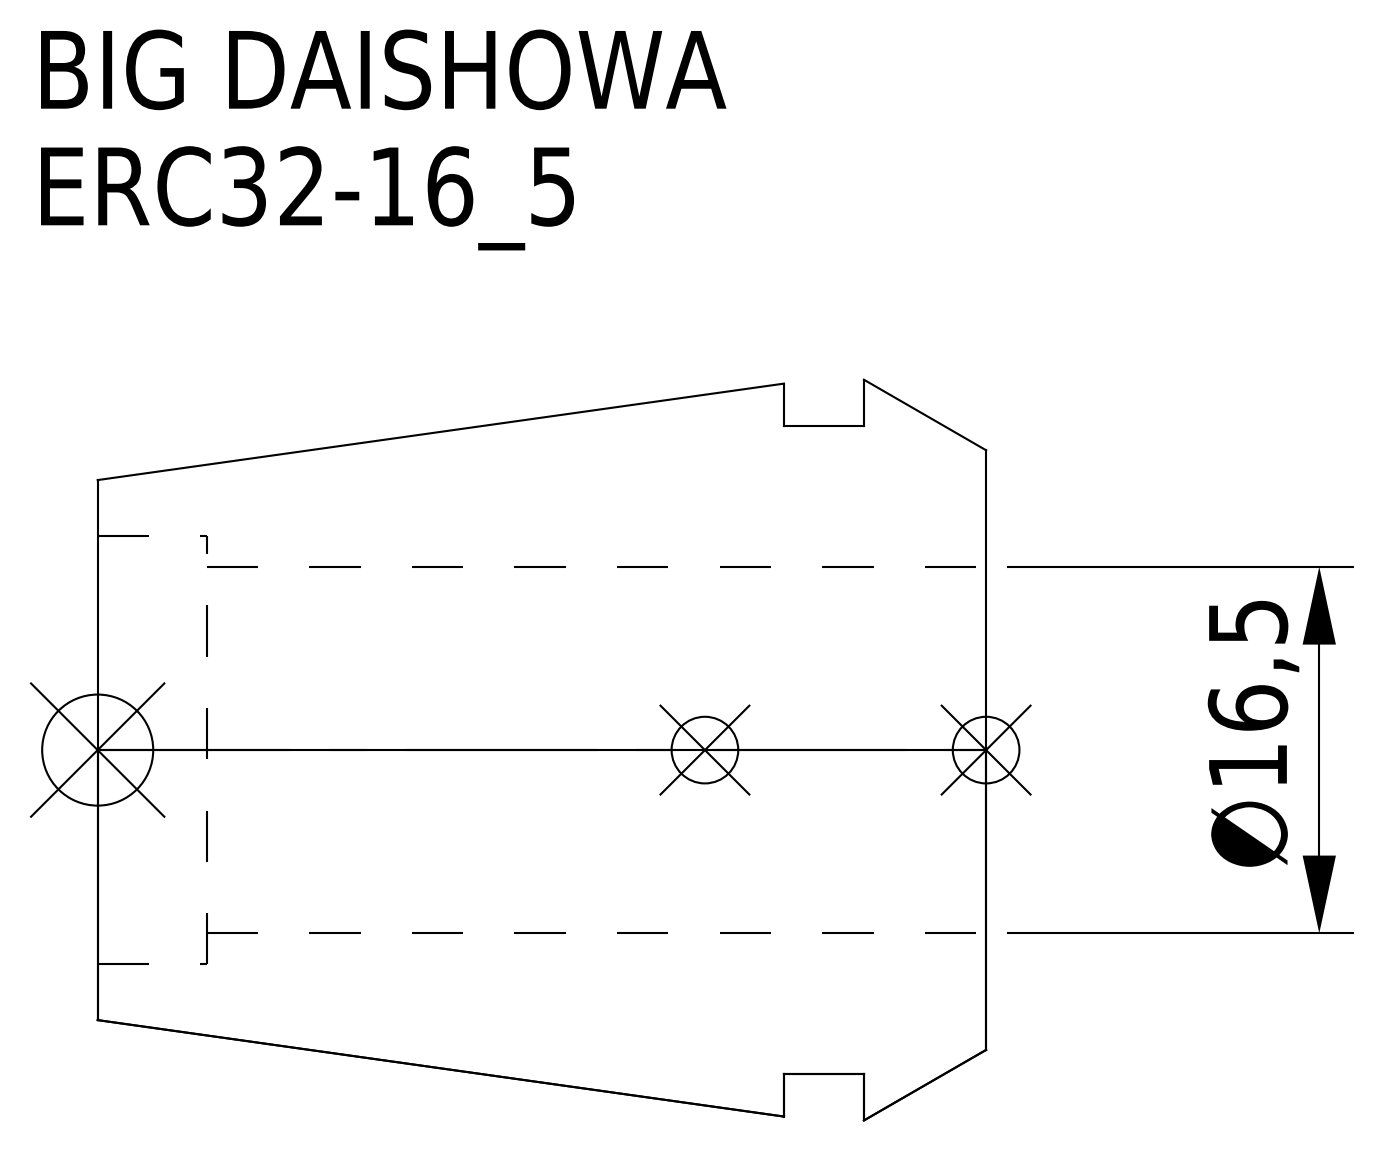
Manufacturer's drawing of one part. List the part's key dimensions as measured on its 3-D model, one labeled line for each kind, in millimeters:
Part name (STEP PRODUCT): ERC32-16_5
STEP written by: CREO PARAMETRIC BY PTC INC, 2016380 (AUTOMOTIVE_DESIGN)
Units: millimetres
Bodies: 1 solid, 15 faces (5 planar, 6 cylindrical, 4 other)
Overall size (bounding box): 40 × 33.35 × 33.35
Volume: 17 503 mm³ · Surface area: 6 857 mm²
Round holes (diameter × count): ⌀16.5 ×1, ⌀19.3 ×1
Round bosses / shafts (diameter × count): ⌀29.2 ×1
Main face-to-face distances: 5.5, 9.1, 3.6, 40, 34.5, 30.9, 35.1, 29.6, 26, 4.9
